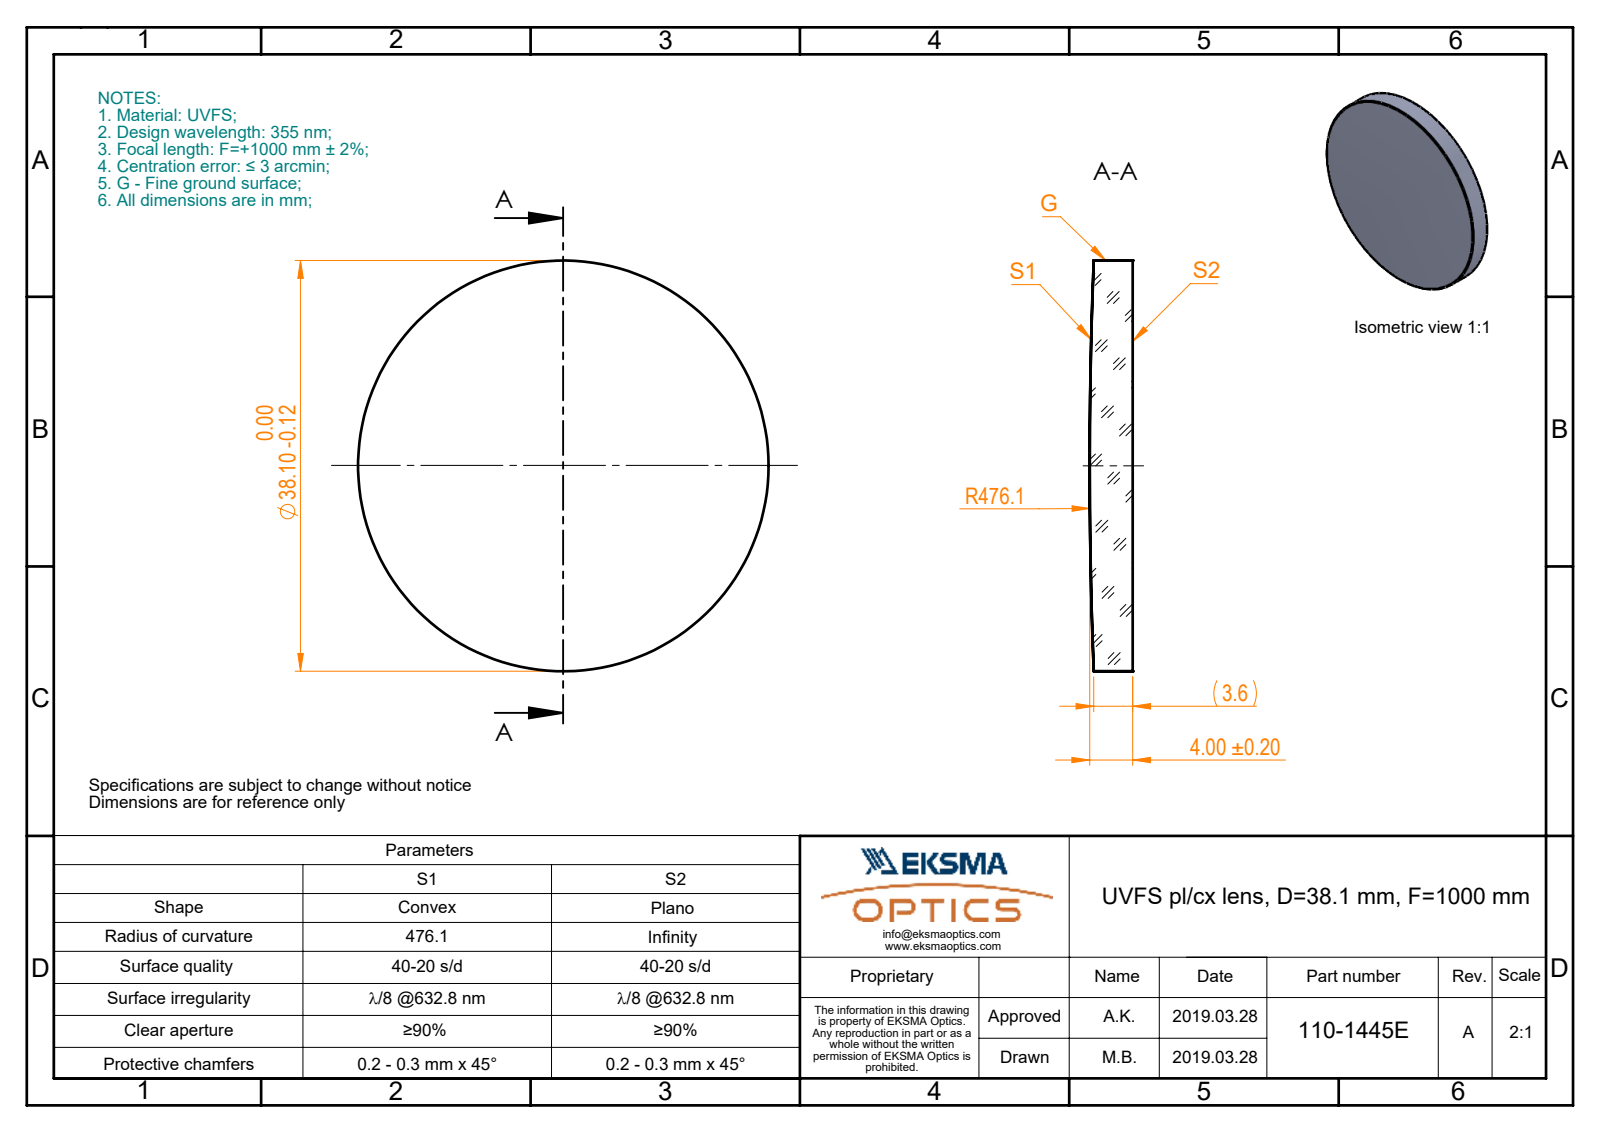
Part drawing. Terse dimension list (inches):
name: 110-1445E UVFS pl-cx 38.1 F1000
written by: SolidWorks 2017 (CONFIG_CONTROL_DESIGN)
unit: in
bodies: 1 solid, 5 faces (1 planar, 2 cylindrical, 2 other)
size: 1.5 × 1.5 × 0.157
volume: 0.265 in³; area: 4.207 in²
bosses: 1× ⌀1.5
